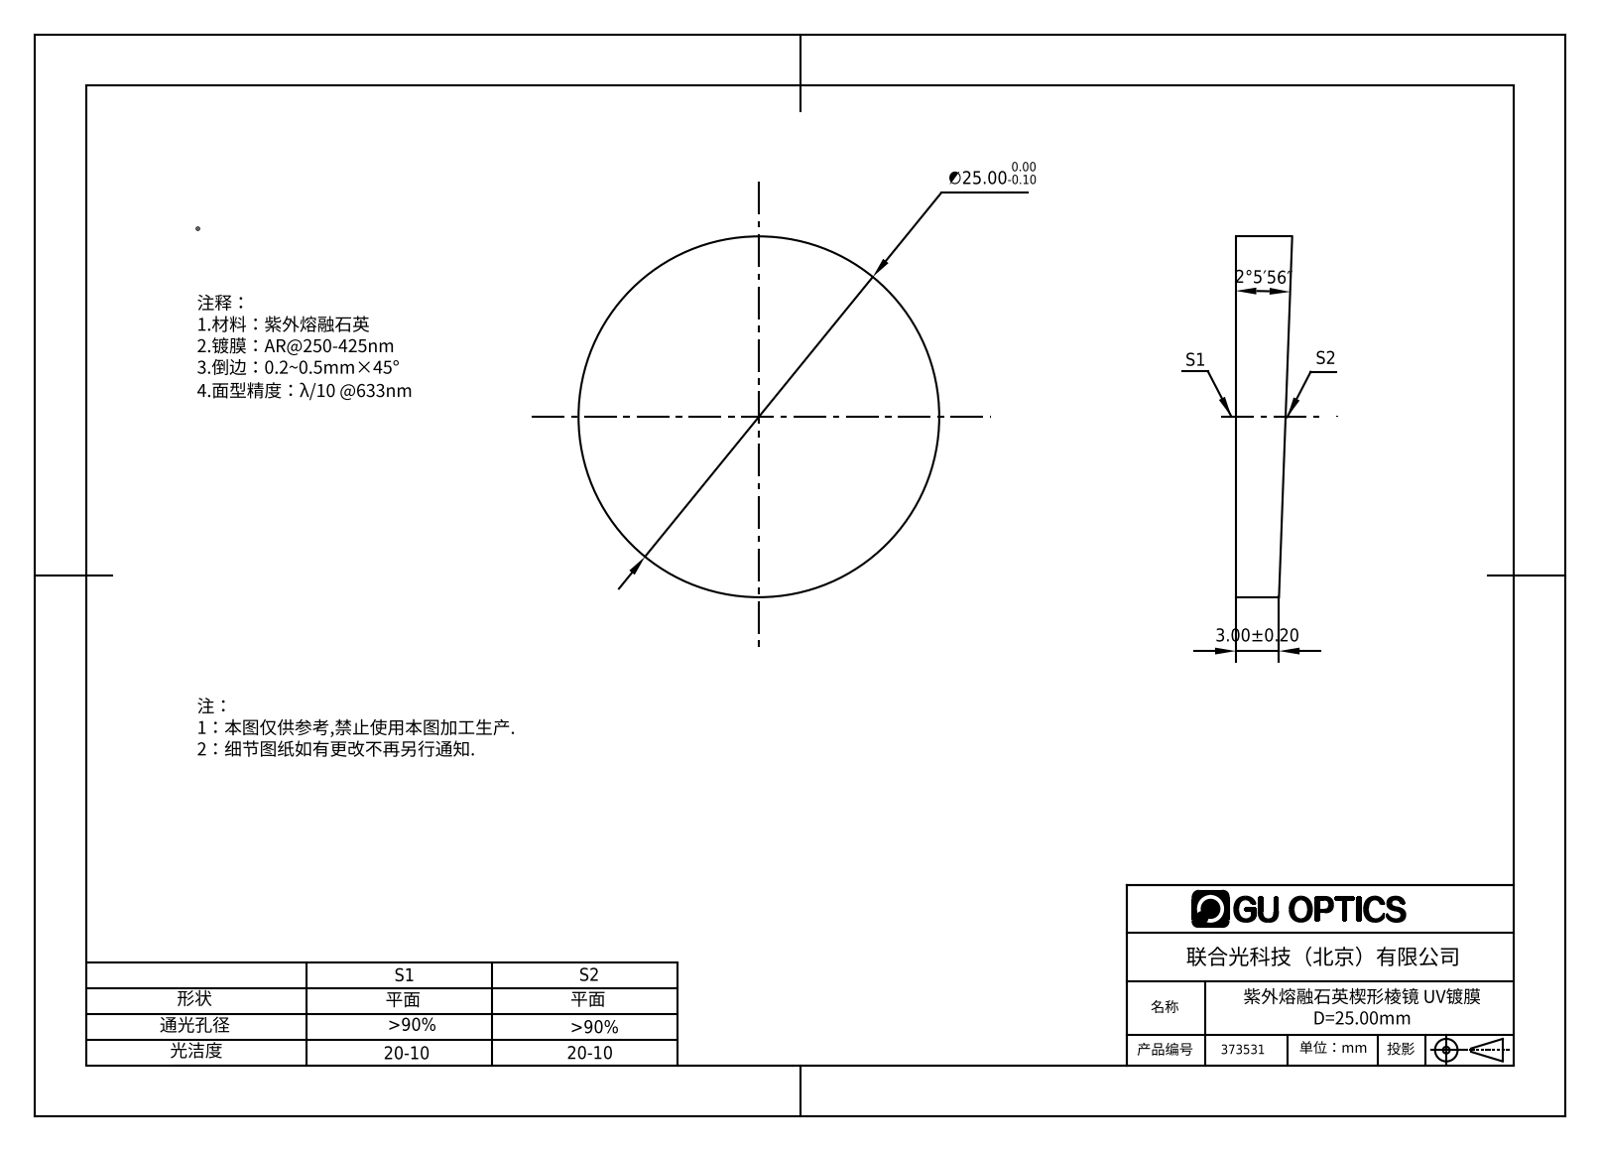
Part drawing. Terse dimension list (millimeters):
name: 373531
written by: SolidWorks 2020 (CONFIG_CONTROL_DESIGN)
unit: mm
bodies: 1 solid, 4 faces (2 planar, 2 cylindrical, 0 other)
size: 25 × 25 × 3.92
volume: 1 697 mm³; area: 1 254 mm²
bosses: 1× ⌀25
